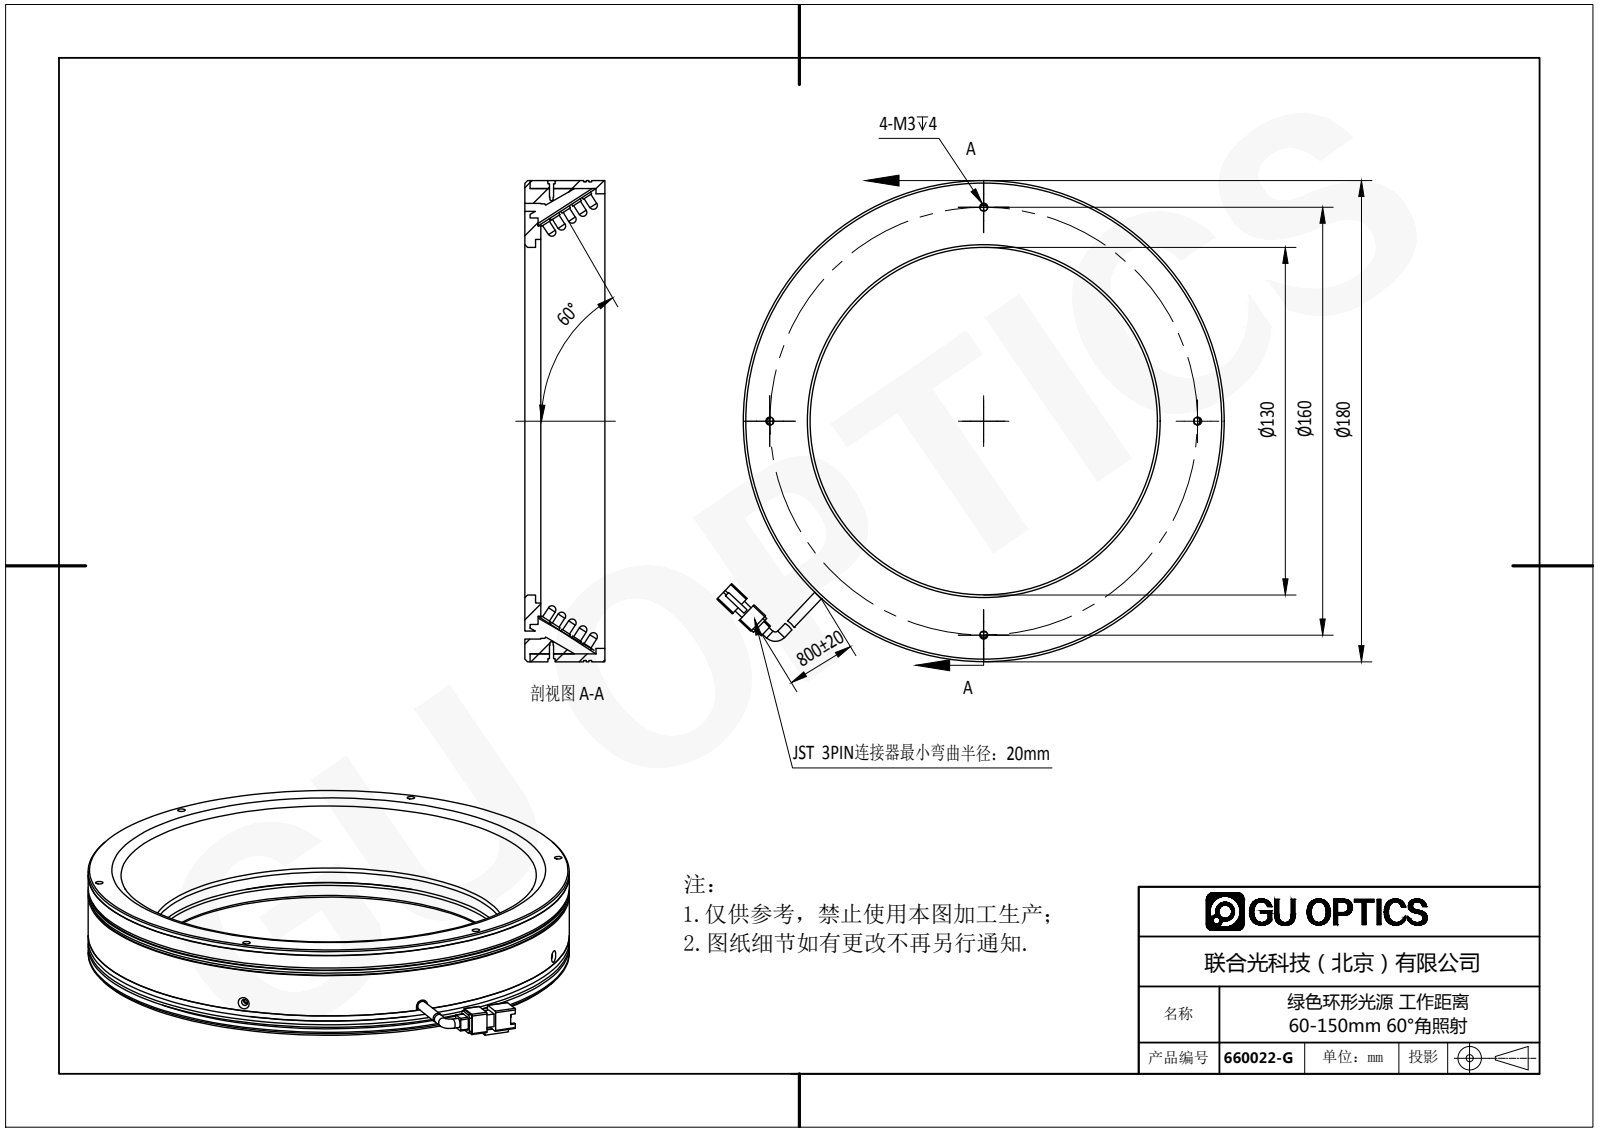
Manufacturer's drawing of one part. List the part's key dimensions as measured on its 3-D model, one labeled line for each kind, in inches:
Part name (STEP PRODUCT): 660022-G
STEP written by: SolidWorks 2016 (AUTOMOTIVE_DESIGN)
Units: inches
Bodies: 506 solids, 8844 faces (6099 planar, 2169 cylindrical, 576 other)
Overall size (bounding box): 7.473 × 7.087 × 1.339
Volume: 12.51 in³ · Surface area: 308.9 in²
Round holes (diameter × count): ⌀0.063 ×8, ⌀0.049 ×6, ⌀0.059 ×6, ⌀0.11 ×6, ⌀0.138 ×5, ⌀0.098 ×4, ⌀0.118 ×4, ⌀0.094 ×2, ⌀5.118 ×1, ⌀5.157 ×1, ⌀5.354 ×1, ⌀6.693 ×1
Round bosses / shafts (diameter × count): ⌀0.15 ×500, ⌀0.118 ×500, ⌀0.138 ×2, ⌀7.087 ×1, ⌀7.047 ×1, ⌀6.85 ×1, ⌀6.772 ×1, ⌀5.948 ×1
Partial cylindrical surfaces — rounded edges, fillets, slot ends (radius × count): R0.02 ×12, R0.039 ×4, R0.069 ×1, R0.236 ×1
Main face-to-face distances: 0.079, 0.039, 0.138, 0.177, 1.26, 1.024, 0.059, 0.098, 1.201, 0.118
Hole centre spacings: 3.425, 5.933, 6.617, 1.722, 1.773, 3.296, 4.653, 5.696
